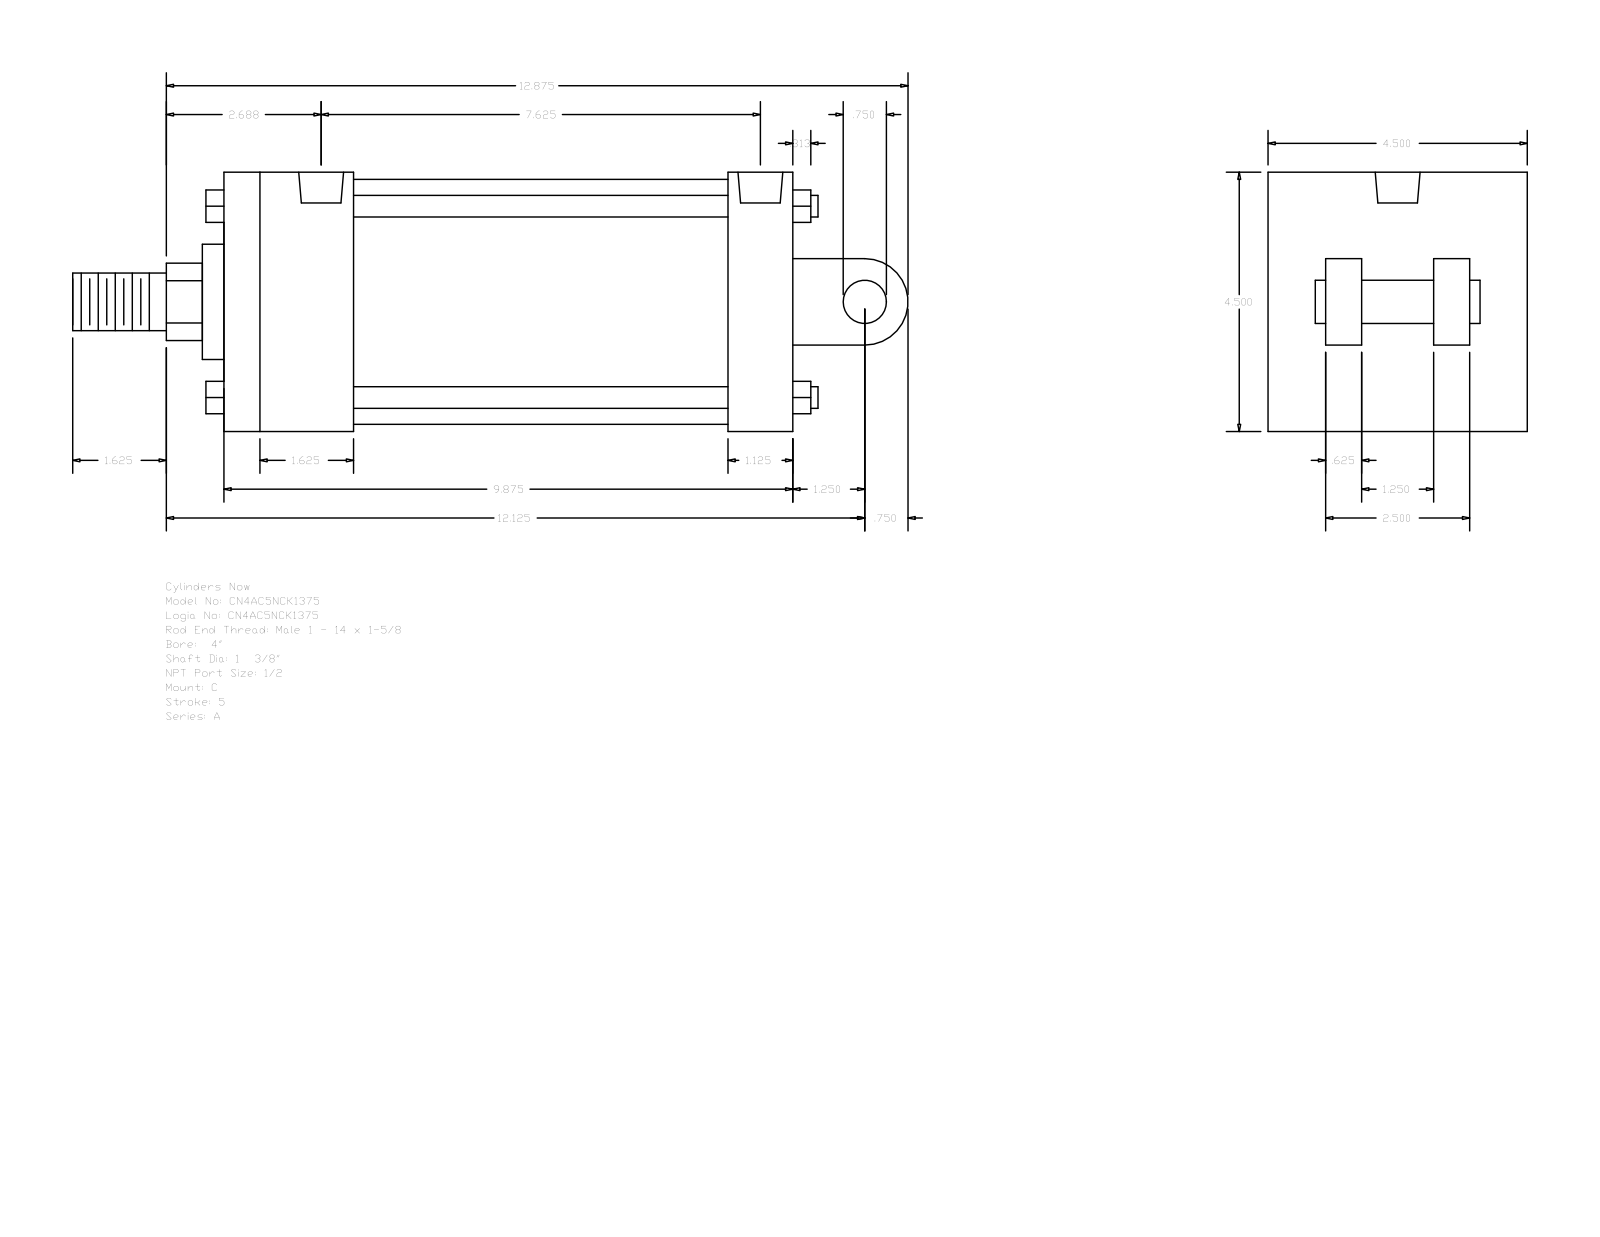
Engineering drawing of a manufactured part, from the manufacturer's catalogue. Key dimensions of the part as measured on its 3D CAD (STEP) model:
Part name (STEP PRODUCT): A_C__0400_1.375
STEP written by: GSSL Pune (CONFIG_CONTROL_DESIGN)
Units: millimetres
Bodies: 0 solids, 135 faces (102 planar, 33 cylindrical, 0 other)
Overall size (bounding box): 368.3 × 114.3 × 114.3
Round holes (diameter × count): ⌀8.73 ×4, ⌀19.77 ×2
Round bosses / shafts (diameter × count): ⌀9.53 ×4, ⌀107.95 ×1, ⌀50.8 ×1, ⌀34.92 ×1, ⌀25.4 ×1, ⌀19.05 ×1
Partial cylindrical surfaces — rounded edges, fillets, slot ends (radius × count): R17.06 ×1, R19.05 ×1
Main face-to-face distances: 114.3, 250.83, 57.15, 28.58, 73.03, 222.25, 165.1, 193.68, 41.27, 25.4
Hole centre spacings: 3.18, 187.32, 190.5, 193.68
